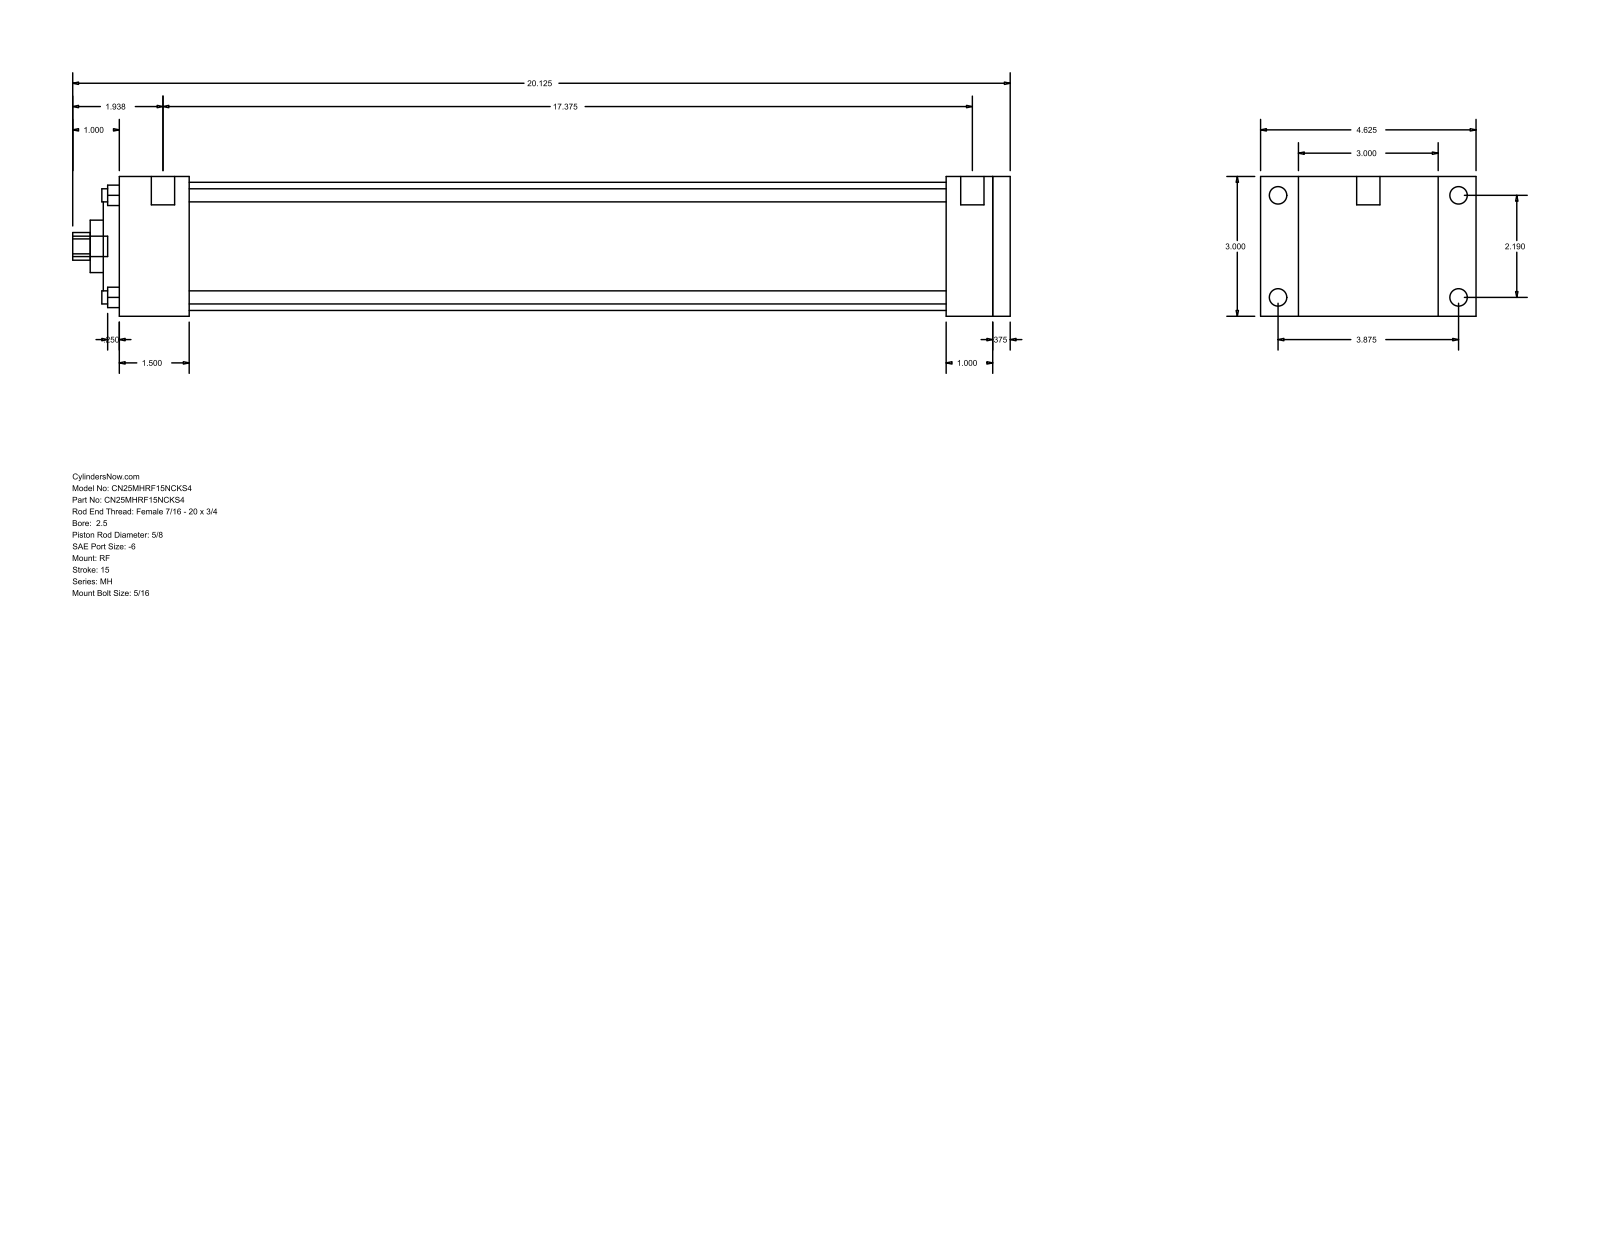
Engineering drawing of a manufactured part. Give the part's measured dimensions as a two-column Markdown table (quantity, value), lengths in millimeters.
| quantity | value |
| --- | --- |
| part name | MH_RF__0250_0.625 |
| STEP written by | GSSL Pune (CONFIG_CONTROL_DESIGN) |
| units | millimeters |
| bodies | 0 solids, 94 faces (65 planar, 29 cylindrical, 0 other) |
| overall size | 511.18 × 117.47 × 76.2 |
| round holes (diameter × count) | 7.14 × 4, 15.88 × 1, 28.57 × 1, 55.55 × 1, 69.85 × 1 |
| round bosses / shafts (diameter × count) | 9.53 × 4, 5.56 × 4, 12.7 × 2, 11.11 × 1 |
| partial cylindrical surfaces (radius × count) | 7.54 × 1 |
| main face-to-face distances | 76.2, 9.53, 485.78, 476.25, 25.4, 450.85, 34.93, 38.1, 412.75, 438.15 |
| hole center spacings | 39.33, 55.62, 78.66 |
